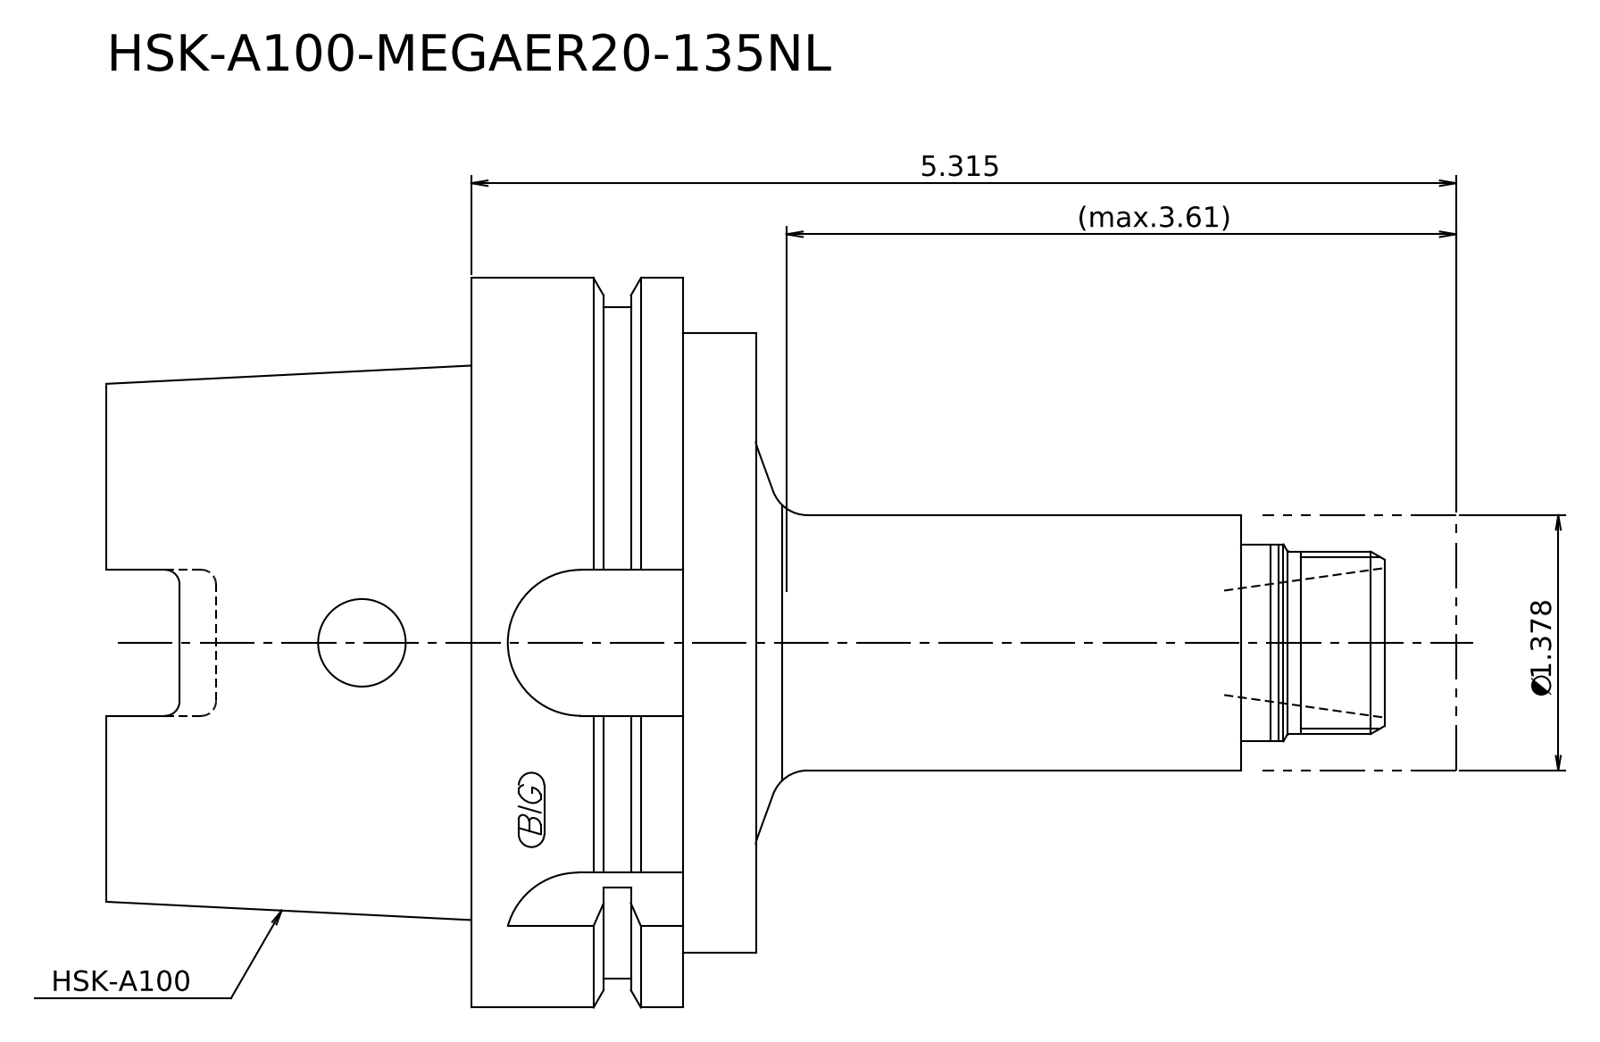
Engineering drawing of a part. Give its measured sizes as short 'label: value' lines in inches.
written by: Kubotek KeyCreator 2011 V10.0.2 (22737) (automotive_design)
unit: in
bodies: 2 solids, 24 faces (10 planar, 8 cylindrical, 6 other)
size: 7.283 × 3.937 × 3.937
volume: 36.34 in³; area: 82.65 in²
bosses: 1× ⌀3.937, 1× ⌀3.622, 1× ⌀3.346, 1× ⌀1.378, 1× ⌀1.063, 1× ⌀0.984
face distances: 1.969, 1.535, 3.504, 0.394, 1.142, 3.11, 2.736, 3.13, 4.272, 6.24
